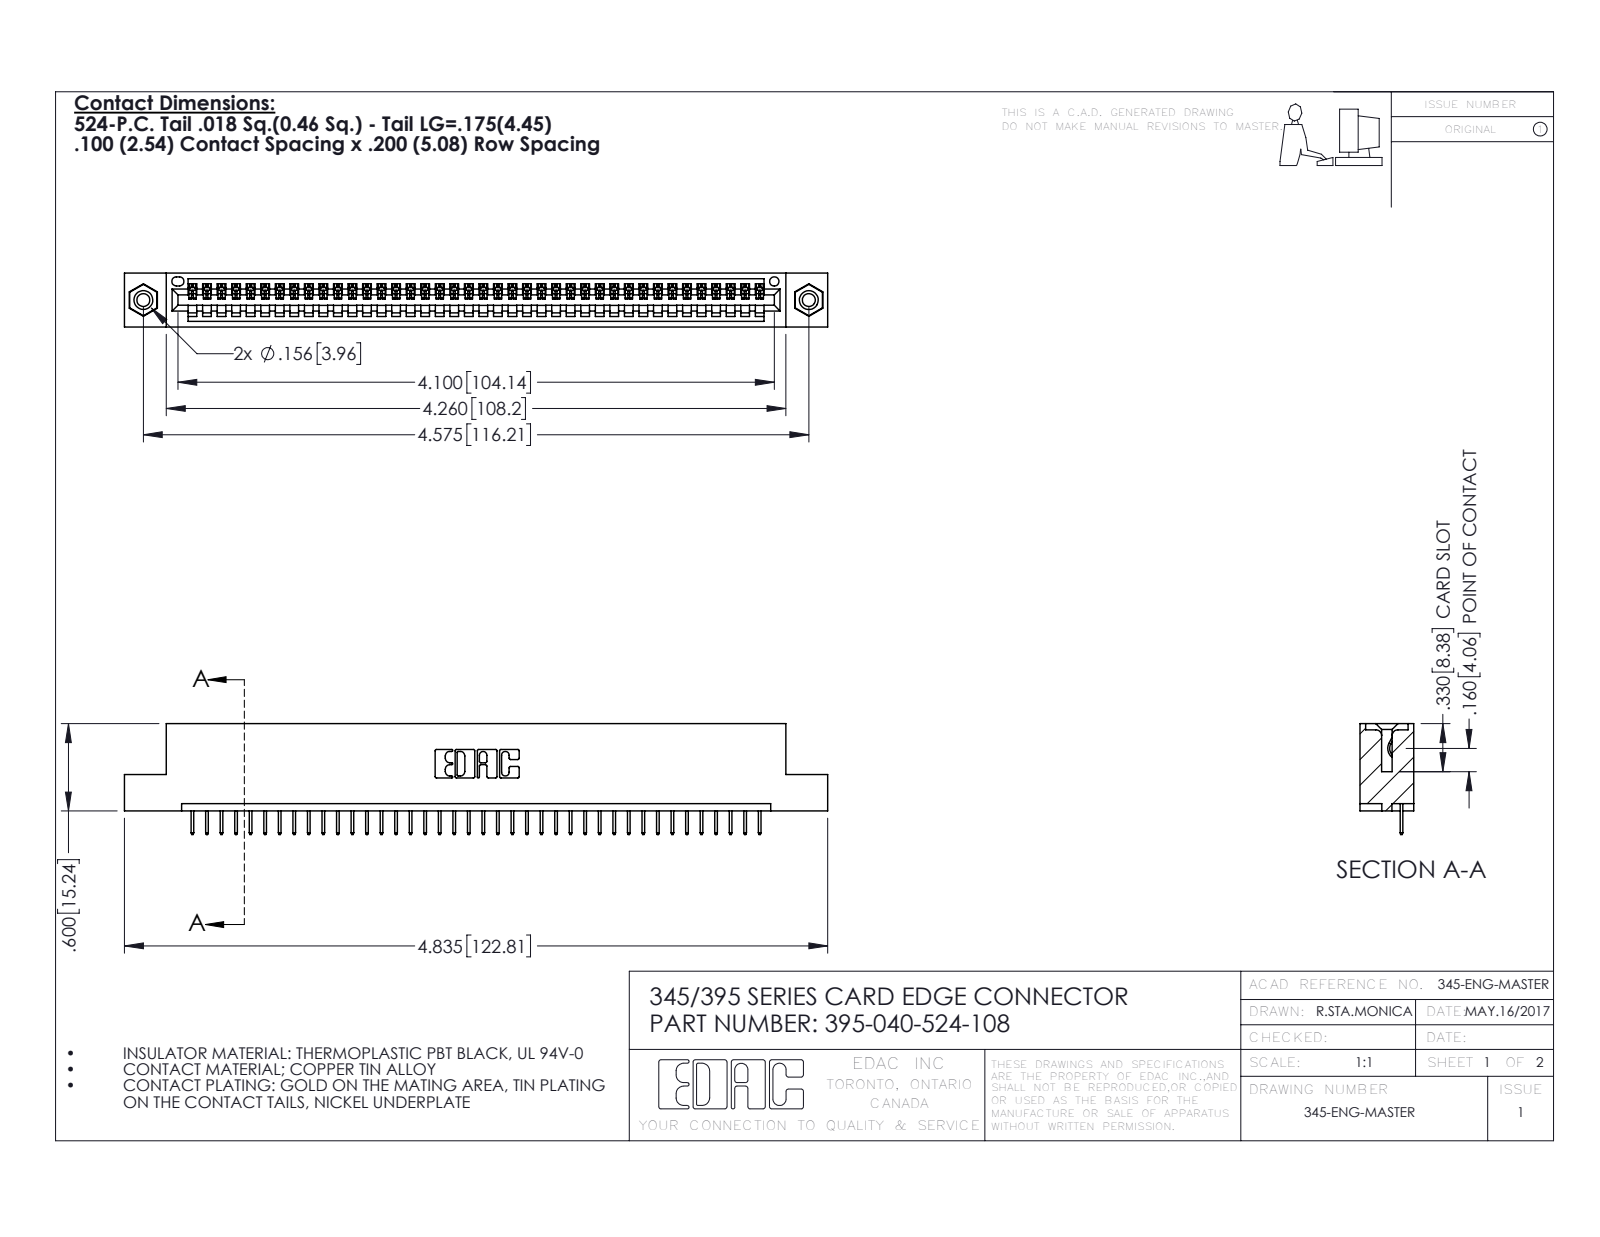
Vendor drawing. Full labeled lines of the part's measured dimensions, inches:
Part name (STEP PRODUCT): 345-292-001_345-293-124; 345 Part_Flush Mounting Lugs - 0.156 Dia-TI; 395-040-524-108; 345-250-001_345-250-003-102
STEP written by: SolidWorks 2016 (CONFIG_CONTROL_DESIGN)
Units: inches
Bodies: 43 solids, 2666 faces (1952 planar, 698 cylindrical, 16 other)
Overall size (bounding box): 4.835 × 0.762 × 0.37
Volume: 0.701 in³ · Surface area: 22.86 in²
Round holes (diameter × count): ⌀0.089 ×2, ⌀0.125 ×2, ⌀0.156 ×2, ⌀0.064 ×1
Round bosses / shafts (diameter × count): ⌀0.155 ×2
Partial cylindrical surfaces — rounded edges, fillets, slot ends (radius × count): R0.006 ×80, R0.01 ×22, R0.007 ×6, R0.031 ×6, R0.026 ×3, R0.031 ×2, R0.04 ×2, R0.014 ×1
Main face-to-face distances: 0.072, 0.298, 0.37, 0.2, 0.098, 0.272, 0.025, 0.225, 0.072, 0.149
Hole centre spacings: 0.27, 4.339, 4.575
